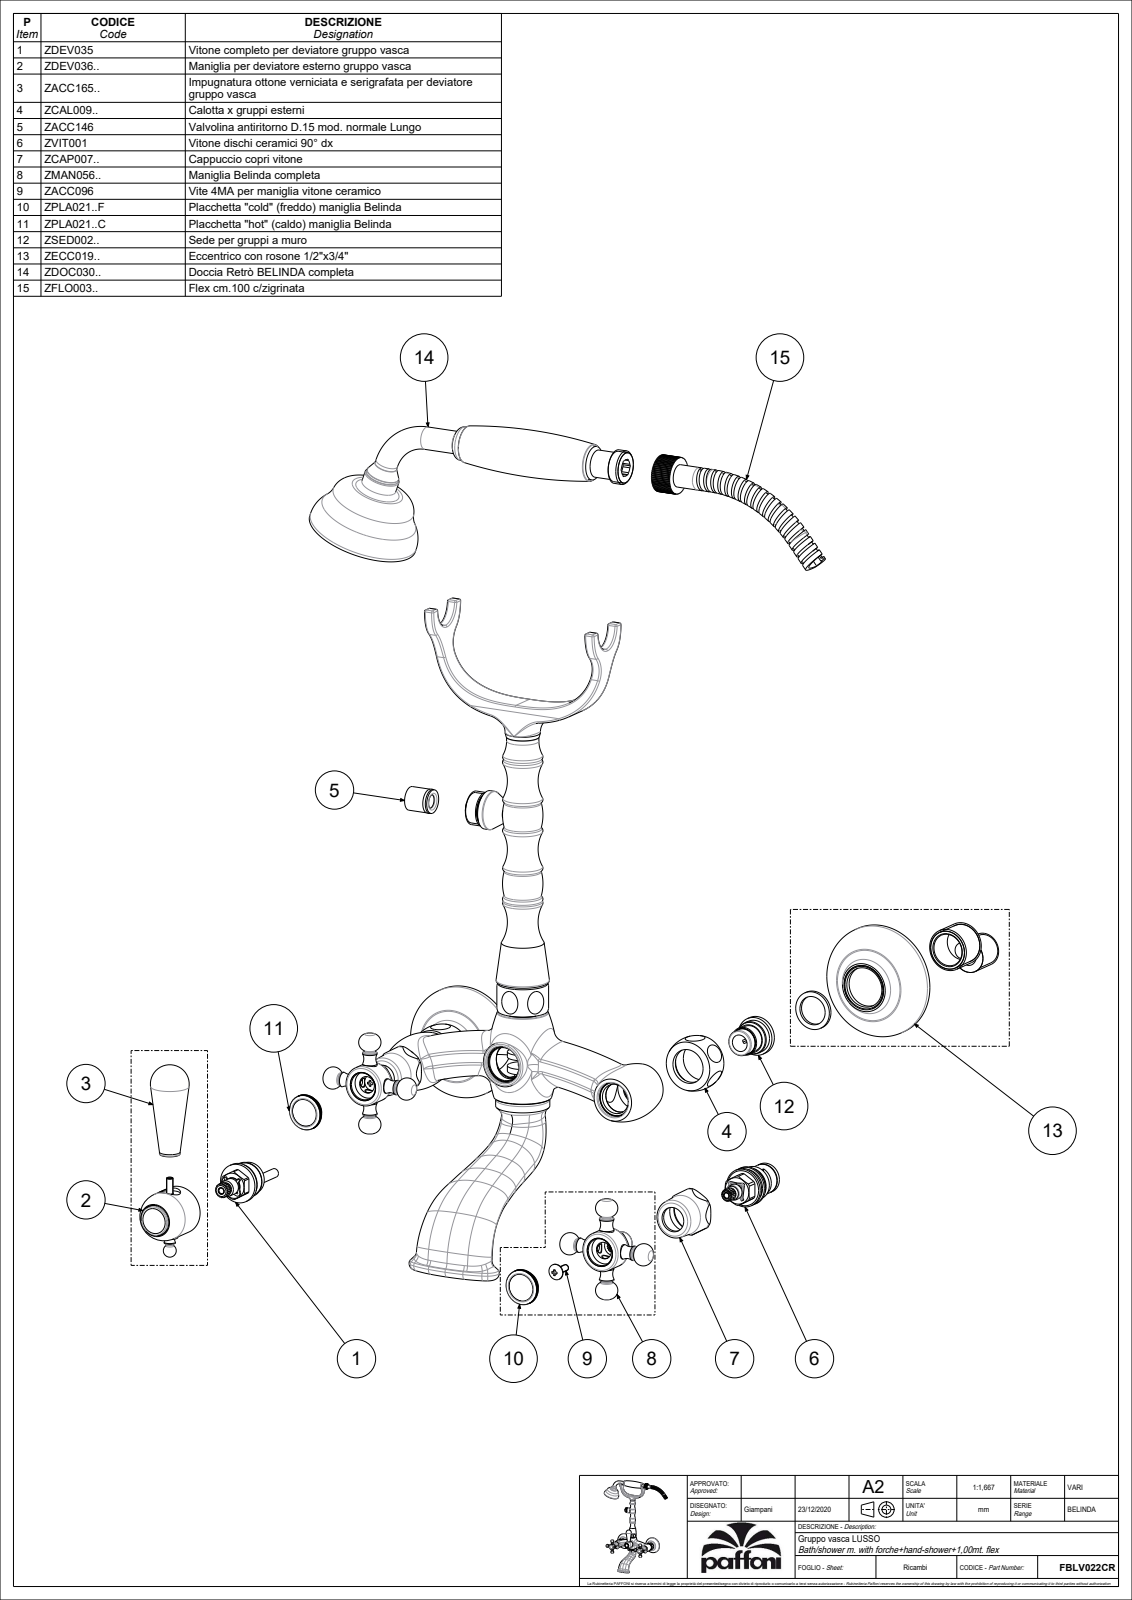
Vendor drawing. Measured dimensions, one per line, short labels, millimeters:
name: FBLV022CR
written by: CREO PARAMETRIC BY PTC INC, 2020044 (CONFIG_CONTROL_DESIGN)
unit: mm
bodies: 7 solids, 2194 faces (713 planar, 600 cylindrical, 881 other)
size: 424 × 331.59 × 169.62
volume: 466 802 mm³; area: 215 233 mm²
holes: 45× ⌀1.2, 4× ⌀19, 3× ⌀15.5, 3× ⌀21.5, 3× ⌀24.1, 3× ⌀27.5, 2× ⌀15, 2× ⌀16.7, 2× ⌀18.63, 2× ⌀21, 2× ⌀22.8, 2× ⌀25
bosses: 4× ⌀14, 3× ⌀9, 3× ⌀7, 2× ⌀70, 2× ⌀28.14, 2× ⌀21, 2× ⌀13, 1× ⌀69
rounds: 8× R1, 2× R3.5, 2× R11, 2× R20, 2× R67.77, 1× R4, 1× R4.5, 1× R5
face distances: 1, 27, 23.5, 18.5, 48, 29.5, 26.92, 8.5, 5, 28.5
hole spacings: 38.08, 33.94, 46.36, 12.42, 24, 41.57, 44.34, 6.27
